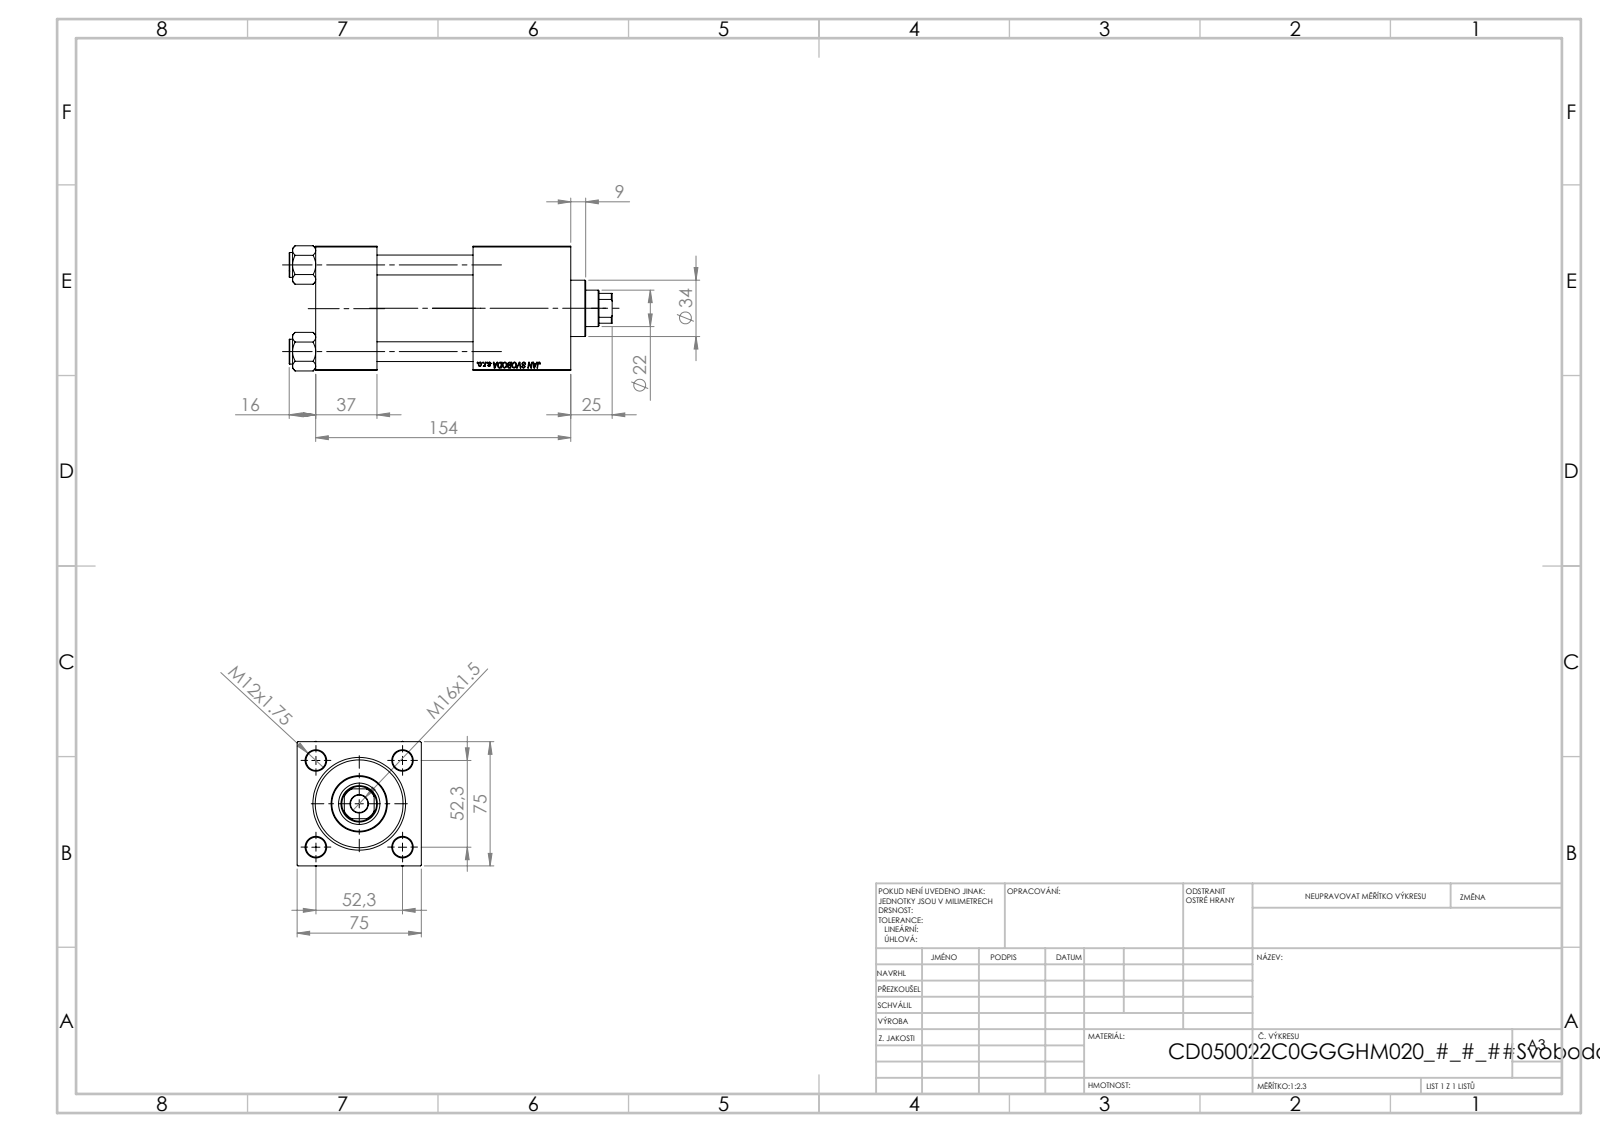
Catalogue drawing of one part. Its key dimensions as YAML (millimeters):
part_name: "NUT_M5_V215CD_C; V215CD_Body_C; V215CD_VCP_C; V215CD_VC_C (+1 more)"
step_written_by: "SolidWorks 2019 (CONFIG_CONTROL_DESIGN)"
units: millimeters
bodies: {solids: 11, faces: 1149, planar: 526, cylindrical: 87, other: 536}
overall_size: [195, 75.54, 75]
volume: 656841
surface_area: 147291
round_holes:
  - {diameter: 12, count: 4}
  - {diameter: 7, count: 2}
  - {diameter: 20.96, count: 2}
  - {diameter: 30, count: 2}
  - {diameter: 10.5, count: 1}
  - {diameter: 22, count: 1}
  - {diameter: 25, count: 1}
  - {diameter: 41, count: 1}
  - {diameter: 50, count: 1}
  - {diameter: 53, count: 1}
round_bosses_or_shafts:
  - {diameter: 15, count: 4}
  - {diameter: 56, count: 1}
  - {diameter: 34, count: 1}
partial_cylinders:
  - {radius: 10.5, count: 1}
face_to_face_distances: [75, 37, 154, 117, 59, 95, 58, 125.3, 88.3, 30.3]
hole_center_spacings: [36.98, 52.3, 73.96, 93.5]
